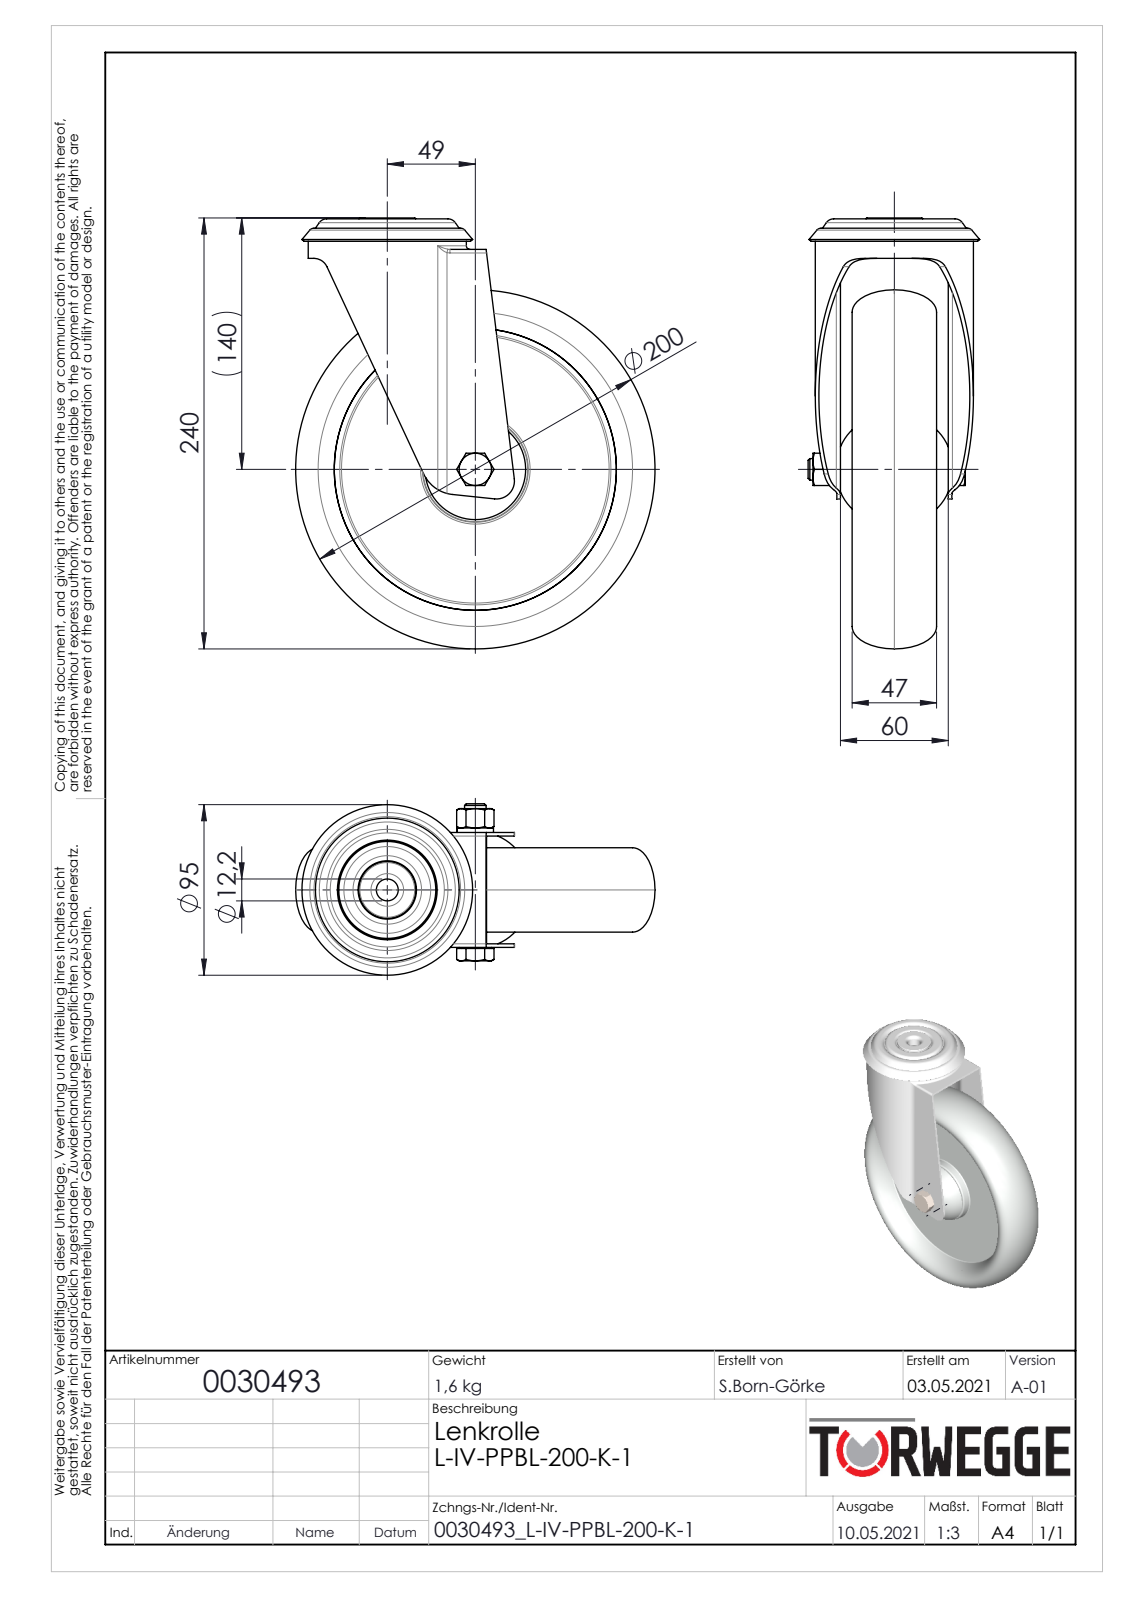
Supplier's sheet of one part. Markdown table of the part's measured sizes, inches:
| quantity | value |
| --- | --- |
| part name | 0030493 |
| STEP written by | SolidWorks 2020 (AUTOMOTIVE_DESIGN) |
| units | inches |
| bodies | 8 solids, 237 faces (63 planar, 54 cylindrical, 120 other) |
| overall size | 9.449 × 7.874 × 3.76 |
| volume | 54.67 in³ |
| surface area | 387.6 in² |
| round holes (diameter × count) | 0.48 × 2, 0.402 × 1, 0.472 × 1, 0.484 × 1, 1.732 × 1, 1.85 × 1, 3.307 × 1 |
| round bosses / shafts (diameter × count) | 3.465 × 1, 1.614 × 1, 1.24 × 1, 0.795 × 1, 0.787 × 1, 0.709 × 1 |
| partial cylindrical surfaces (radius × count) | 0.315 × 3, 0.394 × 3, 0.079 × 2, 0.787 × 1 |
| main face-to-face distances | 0.433, 0.079, 1.043, 0.965, 1.398, 2.441, 1.476, 2.362, 2.52, 0.236 |
